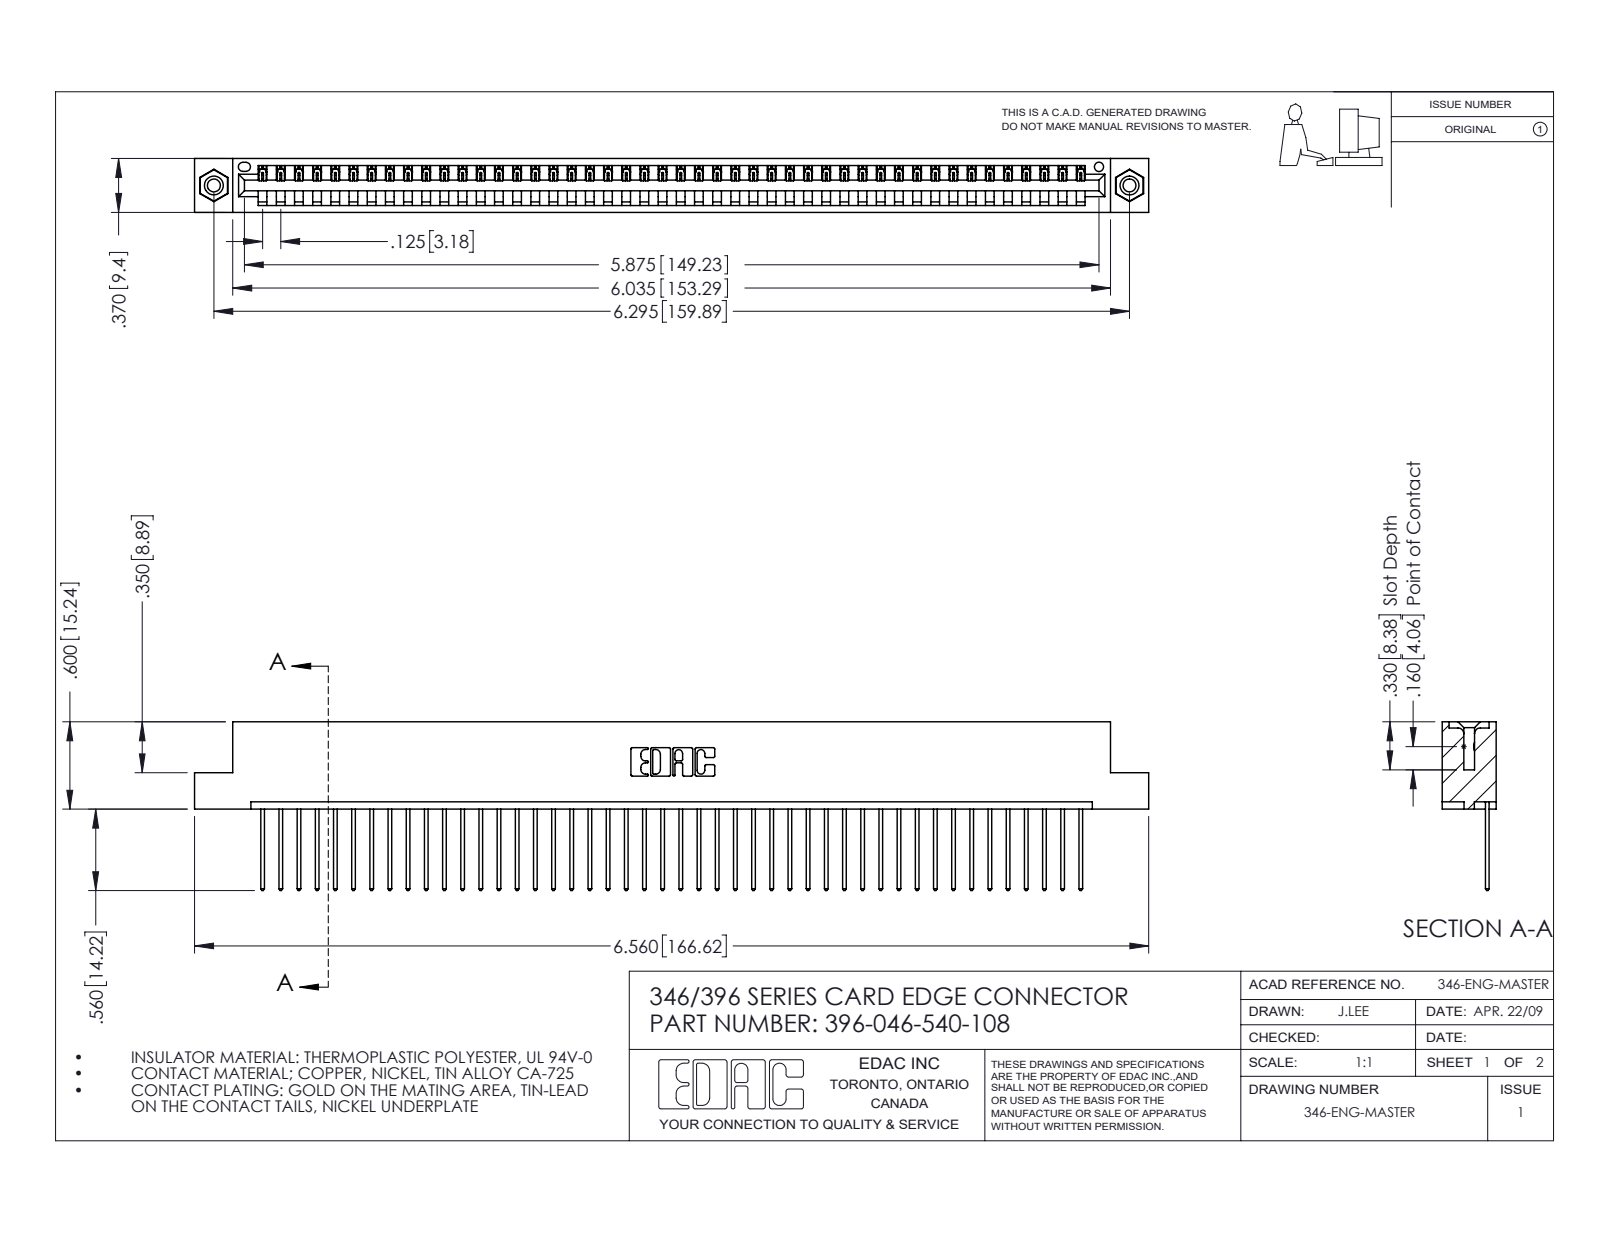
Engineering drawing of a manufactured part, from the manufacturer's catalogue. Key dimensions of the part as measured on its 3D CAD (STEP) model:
Part name (STEP PRODUCT): 345-250-001_345-250-003-102; 346 Part_Flush Mounting Lugs - 0.156 Dia-TI; 345-292-001_345-293-140; 396-046-540-108
STEP written by: SolidWorks 2016 (CONFIG_CONTROL_DESIGN)
Units: inches
Bodies: 49 solids, 2850 faces (1948 planar, 886 cylindrical, 16 other)
Overall size (bounding box): 6.56 × 1.16 × 0.37
Volume: 0.978 in³ · Surface area: 31.87 in²
Round holes (diameter × count): ⌀0.089 ×2, ⌀0.125 ×2, ⌀0.156 ×2, ⌀0.064 ×1
Round bosses / shafts (diameter × count): ⌀0.155 ×2
Partial cylindrical surfaces — rounded edges, fillets, slot ends (radius × count): R0.006 ×92, R0.01 ×92, R0.01 ×22, R0.007 ×6, R0.031 ×6, R0.026 ×3, R0.031 ×2, R0.04 ×2
Main face-to-face distances: 0.048, 0.322, 0.37, 0.25, 0.072, 0.298, 0.025, 0.148, 0.222, 0.1
Hole centre spacings: 0.246, 6.086, 6.295
